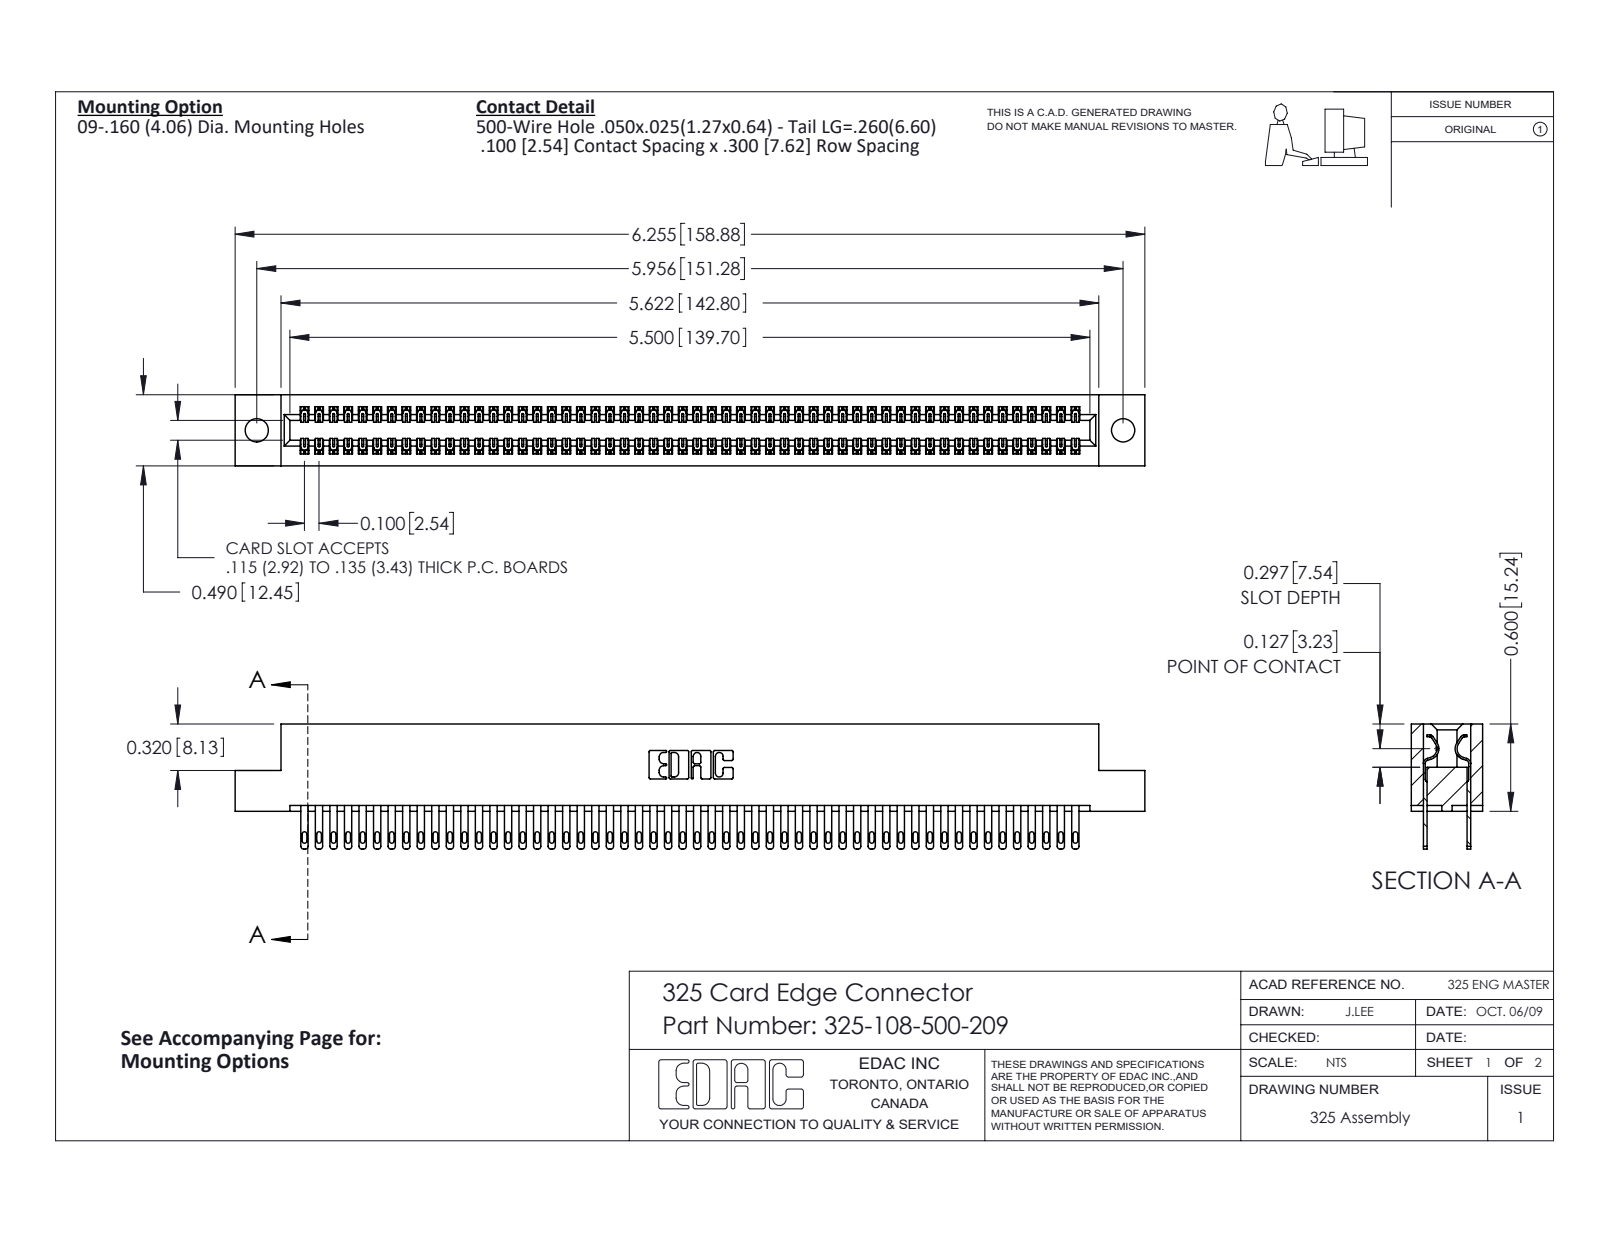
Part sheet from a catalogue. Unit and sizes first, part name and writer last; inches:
Units: inches
Overall size (bounding box): 6.255 × 0.86 × 0.49
Round holes (diameter × count): ⌀0.16 ×2
Partial cylindrical surfaces — rounded edges, fillets, slot ends (radius × count): R0.006 ×162, R0.016 ×108, R0.02 ×108, R0.01 ×22, R0.007 ×6, R0.031 ×6, R0.026 ×3, R0.014 ×2
Main face-to-face distances: 0.083, 0.407, 0.3, 0.107, 0.383, 0.025, 0.49, 0.325, 0.275, 0.56
Hole centre spacings: 5.956
Volume: 1.264 in³ · Surface area: 40.94 in²
Bodies: 109 solids, 5298 faces (3310 planar, 1988 cylindrical, 0 other)
Part name (STEP PRODUCT): 325 Part_.160 TH; 325-108-500-209; 325-292-001_325-293-100
STEP written by: SolidWorks 2016 (CONFIG_CONTROL_DESIGN)
